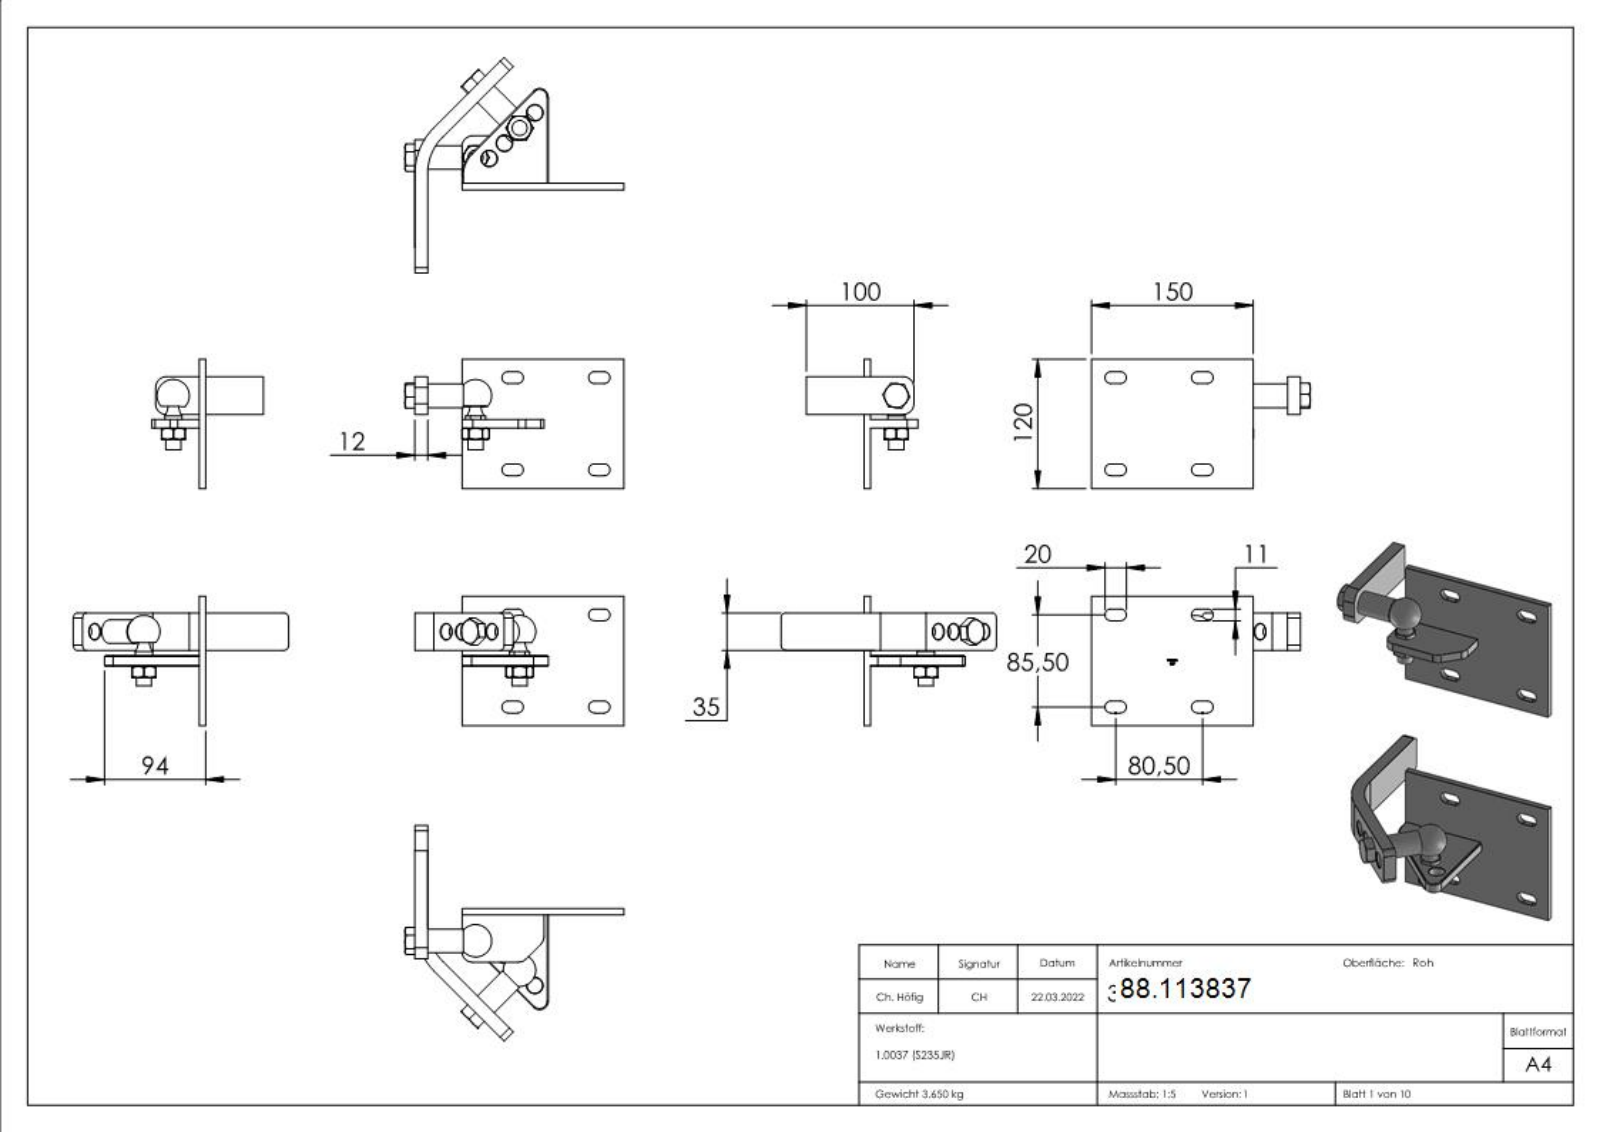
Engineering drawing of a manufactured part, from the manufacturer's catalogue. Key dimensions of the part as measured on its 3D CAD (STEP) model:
Part name (STEP PRODUCT): 3837 Teil7_3837 Teil7; 3837 Teil1_3837 Teil1; 3837 Teil2_3837 Teil2; 3837 Teil8_3837 Teil8 (+5 more)
STEP written by: SolidWorks 2018 (CONFIG_CONTROL_DESIGN)
Units: millimetres
Bodies: 12 solids, 574 faces (198 planar, 75 cylindrical, 301 other)
Overall size (bounding box): 340 × 203 × 200
Volume: 467 971 mm³ · Surface area: 162 190 mm²
Round holes (diameter × count): ⌀14.5 ×10, ⌀12 ×4, ⌀19.5 ×2
Round bosses / shafts (diameter × count): ⌀14 ×4, ⌀22.36 ×2, ⌀22 ×2, ⌀14.1 ×2, ⌀13 ×2
Partial cylindrical surfaces — rounded edges, fillets, slot ends (radius × count): R5.5 ×16, R0.5 ×12, R10 ×5, R5 ×4, R9.4 ×2, R8 ×1, R30 ×1, R48 ×1
Main face-to-face distances: 6, 12, 219, 35, 10, 39.66, 4.66, 221, 11.86, 12.14
Hole centre spacings: 20, 39.99, 40, 12.64, 29.86, 49.23, 59.99, 60
